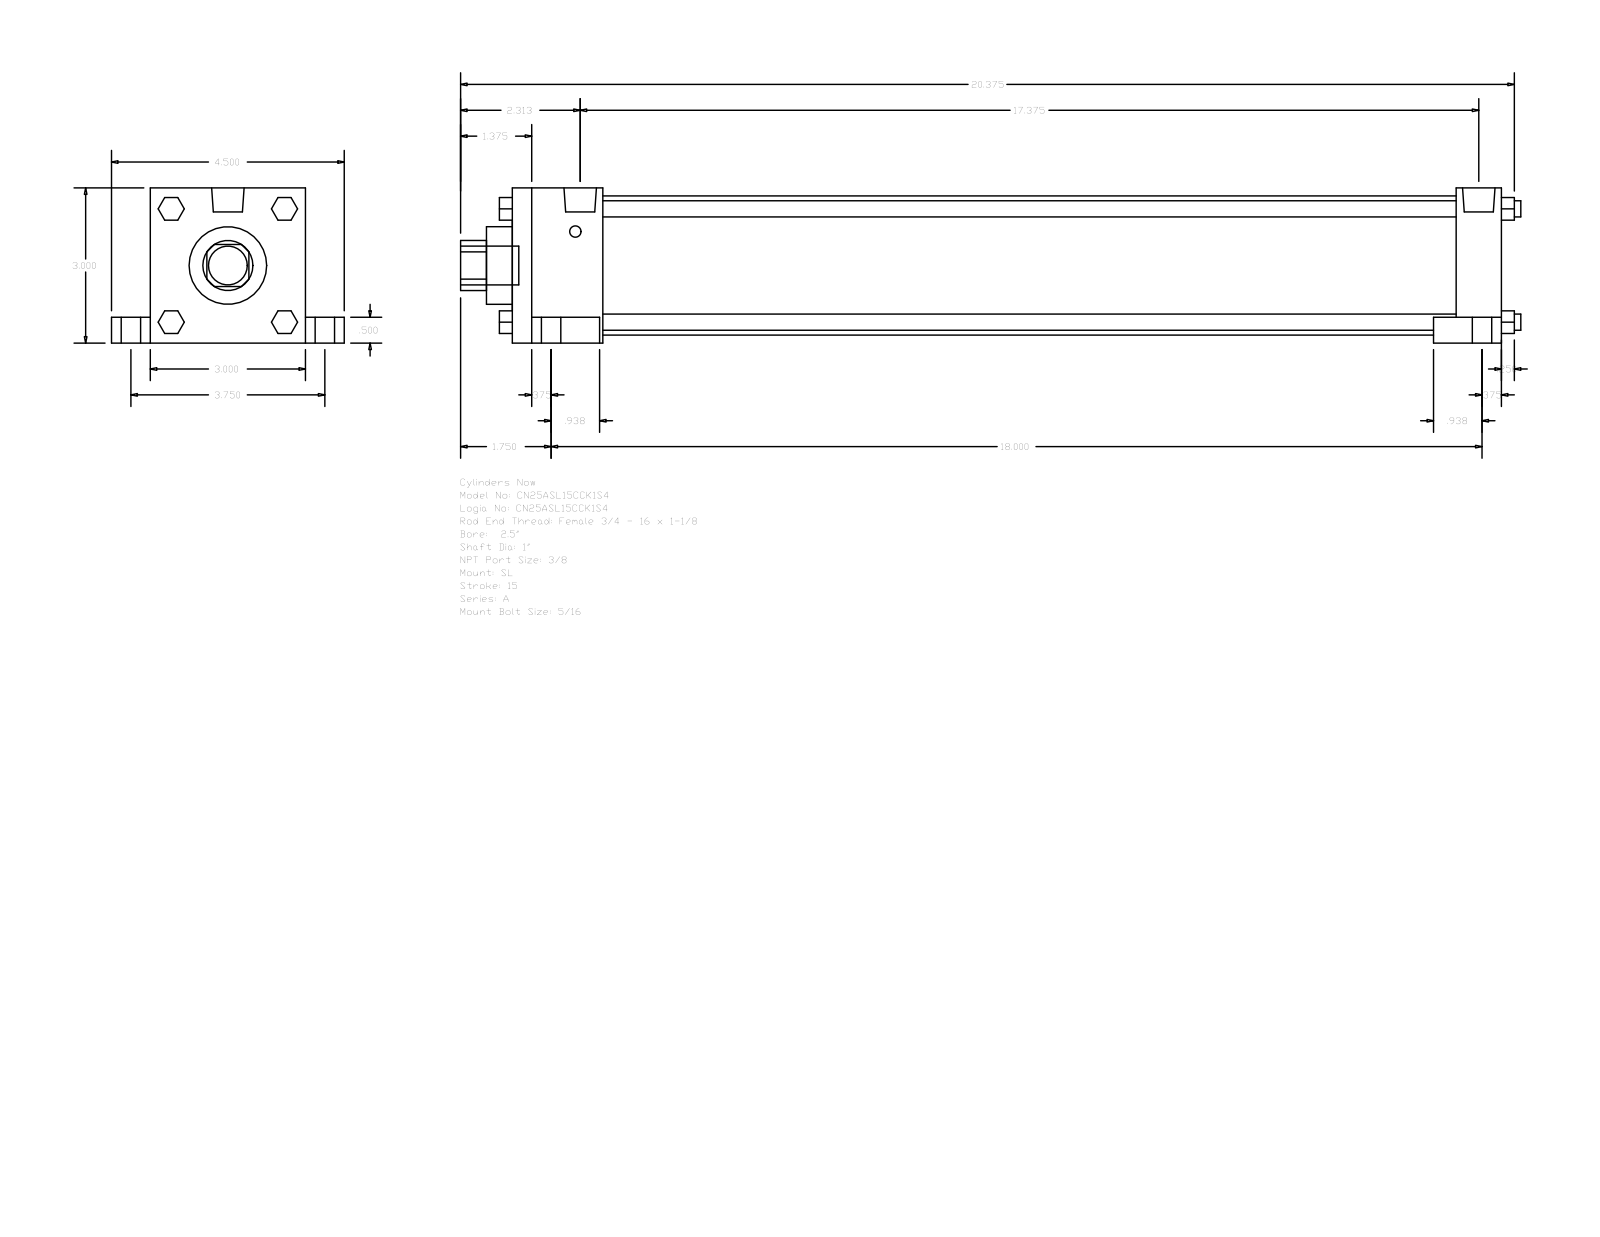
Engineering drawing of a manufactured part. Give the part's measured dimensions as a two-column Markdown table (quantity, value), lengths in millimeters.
| quantity | value |
| --- | --- |
| part name | A_SL__0250_1 |
| STEP written by | GSSL Pune (CONFIG_CONTROL_DESIGN) |
| units | millimeters |
| bodies | 0 solids, 148 faces (112 planar, 36 cylindrical, 0 other) |
| overall size | 520.7 × 114.3 × 76.2 |
| round holes (diameter × count) | 25.4 × 1, 38.1 × 1, 68.33 × 1 |
| round bosses / shafts (diameter × count) | 15.88 × 4, 9.53 × 4, 7.94 × 4, 5.56 × 4, 15.93 × 2, 19.05 × 1 |
| partial cylindrical surfaces (radius × count) | 12.29 × 1 |
| main face-to-face distances | 76.2, 485.78, 12.7, 44.45, 441.33, 463.55, 419.1, 22.23, 19.05, 63.5 |
